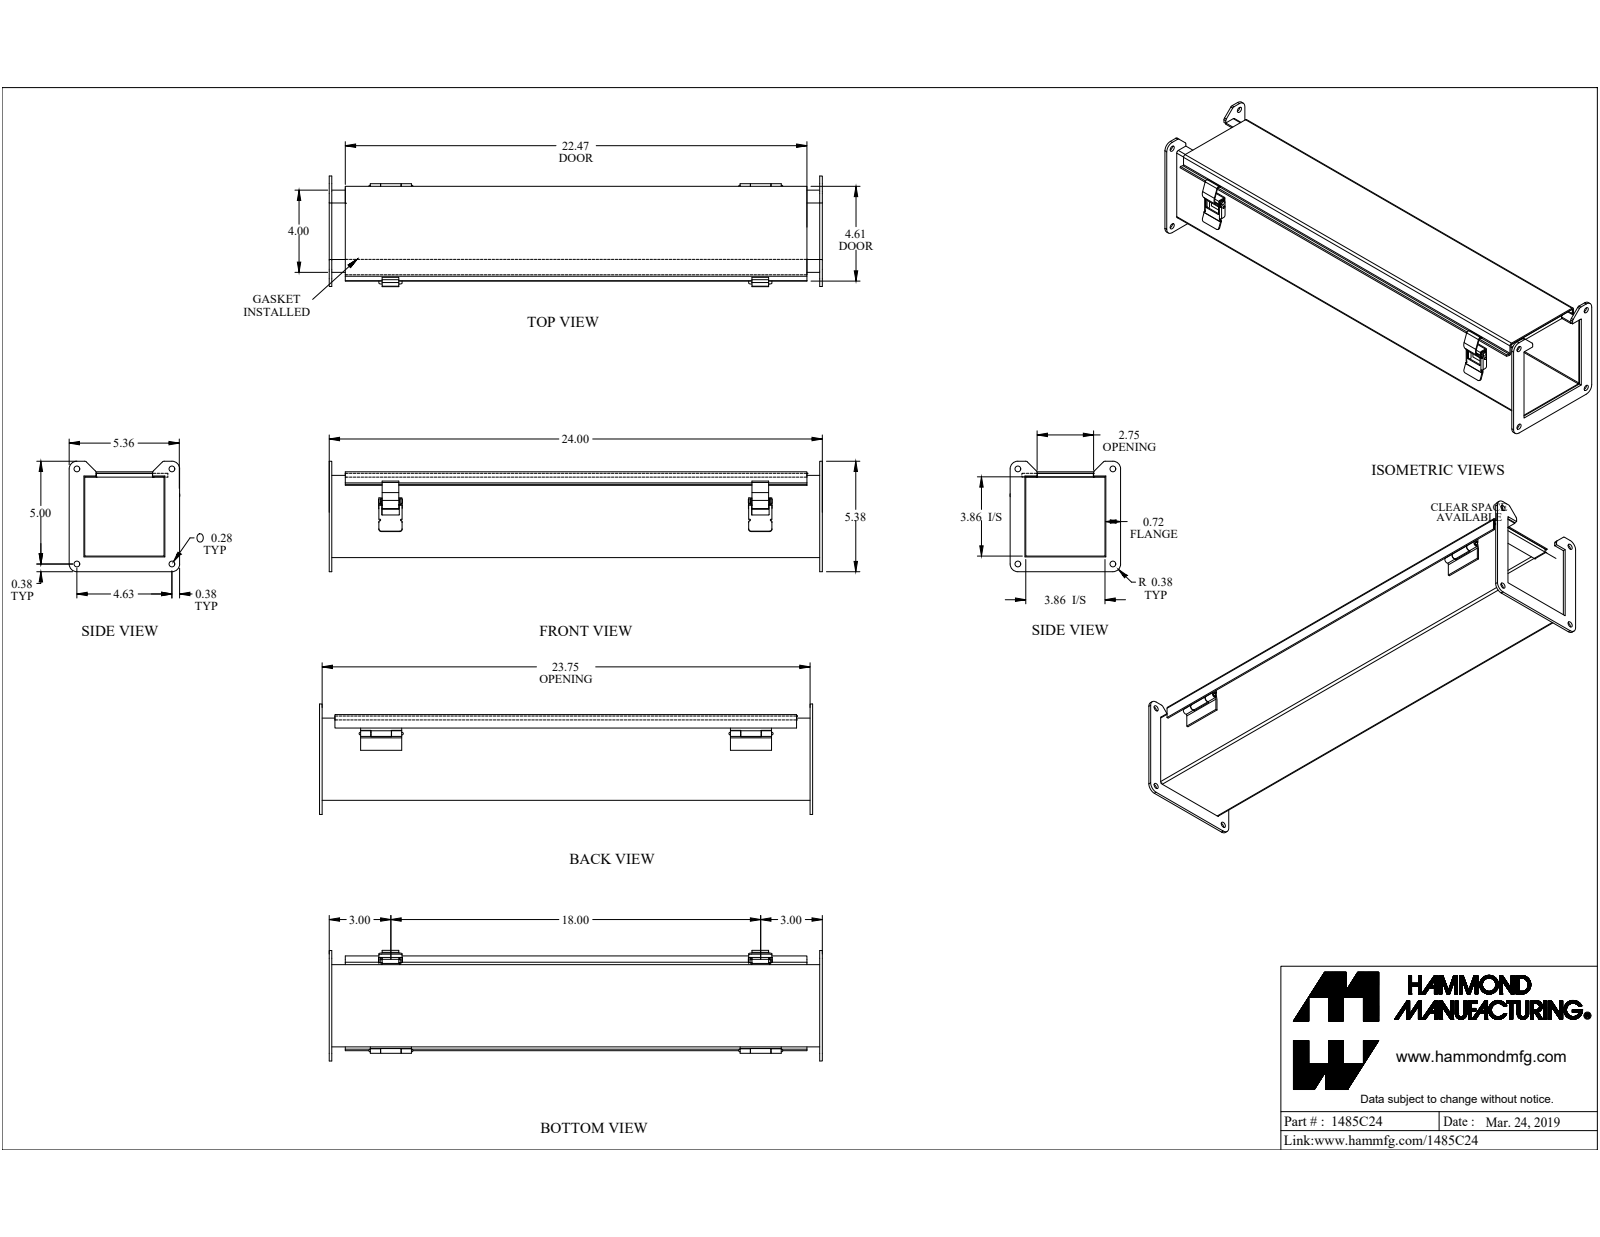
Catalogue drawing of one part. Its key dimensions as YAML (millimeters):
part_name: "1485C24"
step_written_by: "SolidWorks 2019 (CONFIG_CONTROL_DESIGN)"
units: millimeters
bodies: {solids: 20, faces: 410, planar: 250, cylindrical: 156, other: 4}
overall_size: [609.6, 136.7, 136.5]
volume: 689400
surface_area: 685200
round_holes:
  - {diameter: 7.1, count: 4}
  - {diameter: 3.2, count: 1}
  - {diameter: 3.3, count: 1}
  - {diameter: 4.2, count: 1}
round_bosses_or_shafts:
  - {diameter: 4.7, count: 2}
  - {diameter: 7, count: 1}
  - {diameter: 4, count: 1}
  - {diameter: 3.2, count: 1}
partial_cylinders:
  - {radius: 0.4, count: 13}
  - {radius: 3.2, count: 9}
  - {radius: 0.9, count: 7}
  - {radius: 2.7, count: 7}
  - {radius: 0.9, count: 5}
  - {radius: 1, count: 5}
  - {radius: 1.9, count: 5}
  - {radius: 0.4, count: 4}
face_to_face_distances: [1.8, 99.8, 104.1, 101.6, 97.9, 106, 102.3, 4.4, 99.4, 97.6]
hole_center_spacings: [117.5, 166.1, 7.2, 27.3, 39.9, 47, 70.7, 77.6]
